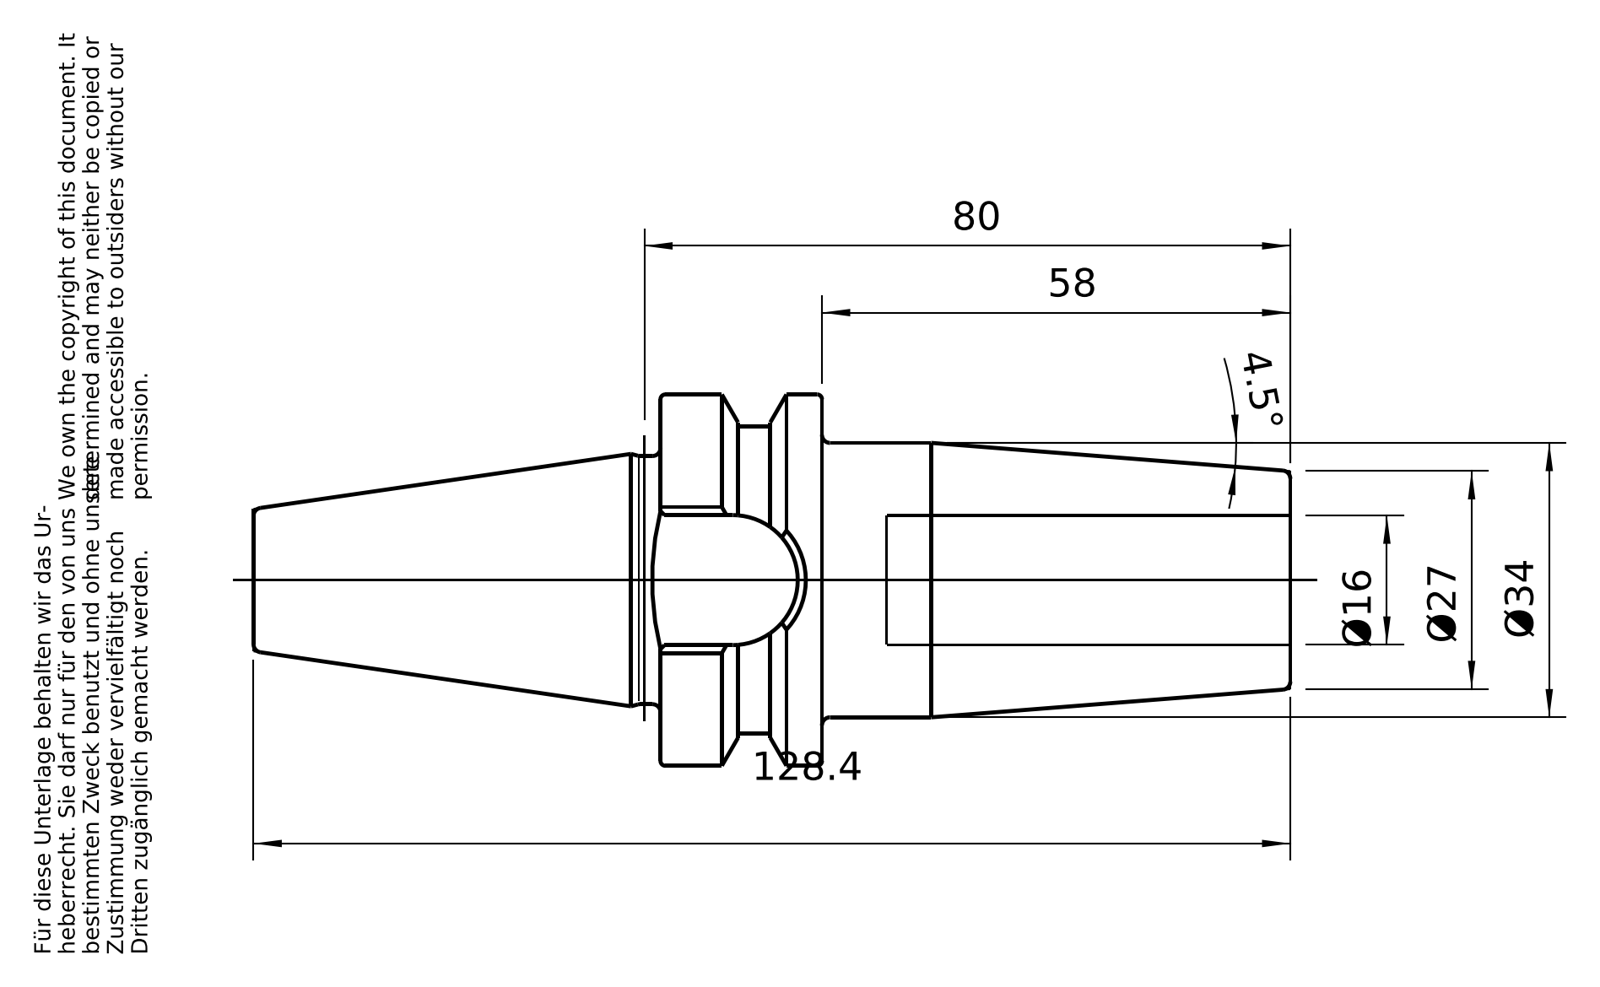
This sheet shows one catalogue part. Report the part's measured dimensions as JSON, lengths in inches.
{"part_name": "30-640-16", "step_written_by": "PRO/ENGINEER BY PARAMETRIC TECHNOLOGY CORPORATION, 2010430 (CONFIG_CONTROL_DESIGN)", "units": "inches", "bodies": {"solids": 1, "faces": 96, "planar": 26, "cylindrical": 22, "other": 48}, "overall_size": [5.055, 1.81, 1.81], "volume_in3": 5.15, "surface_area_in2": 30.48, "round_holes": [[0.398, 1], [0.493, 1], [0.512, 1], [0.63, 1]], "round_bosses_or_shafts": [[1.81, 1], [1.339, 1], [1.211, 1], [0.473, 1]], "partial_cylinders_radius": [[0.319, 1], [0.743, 1]], "face_to_face_distances": [0.787, 3.071, 2.283, 1.272, 1.102, 0.315, 1.969, 0.638, 1.984, 2.772]}
